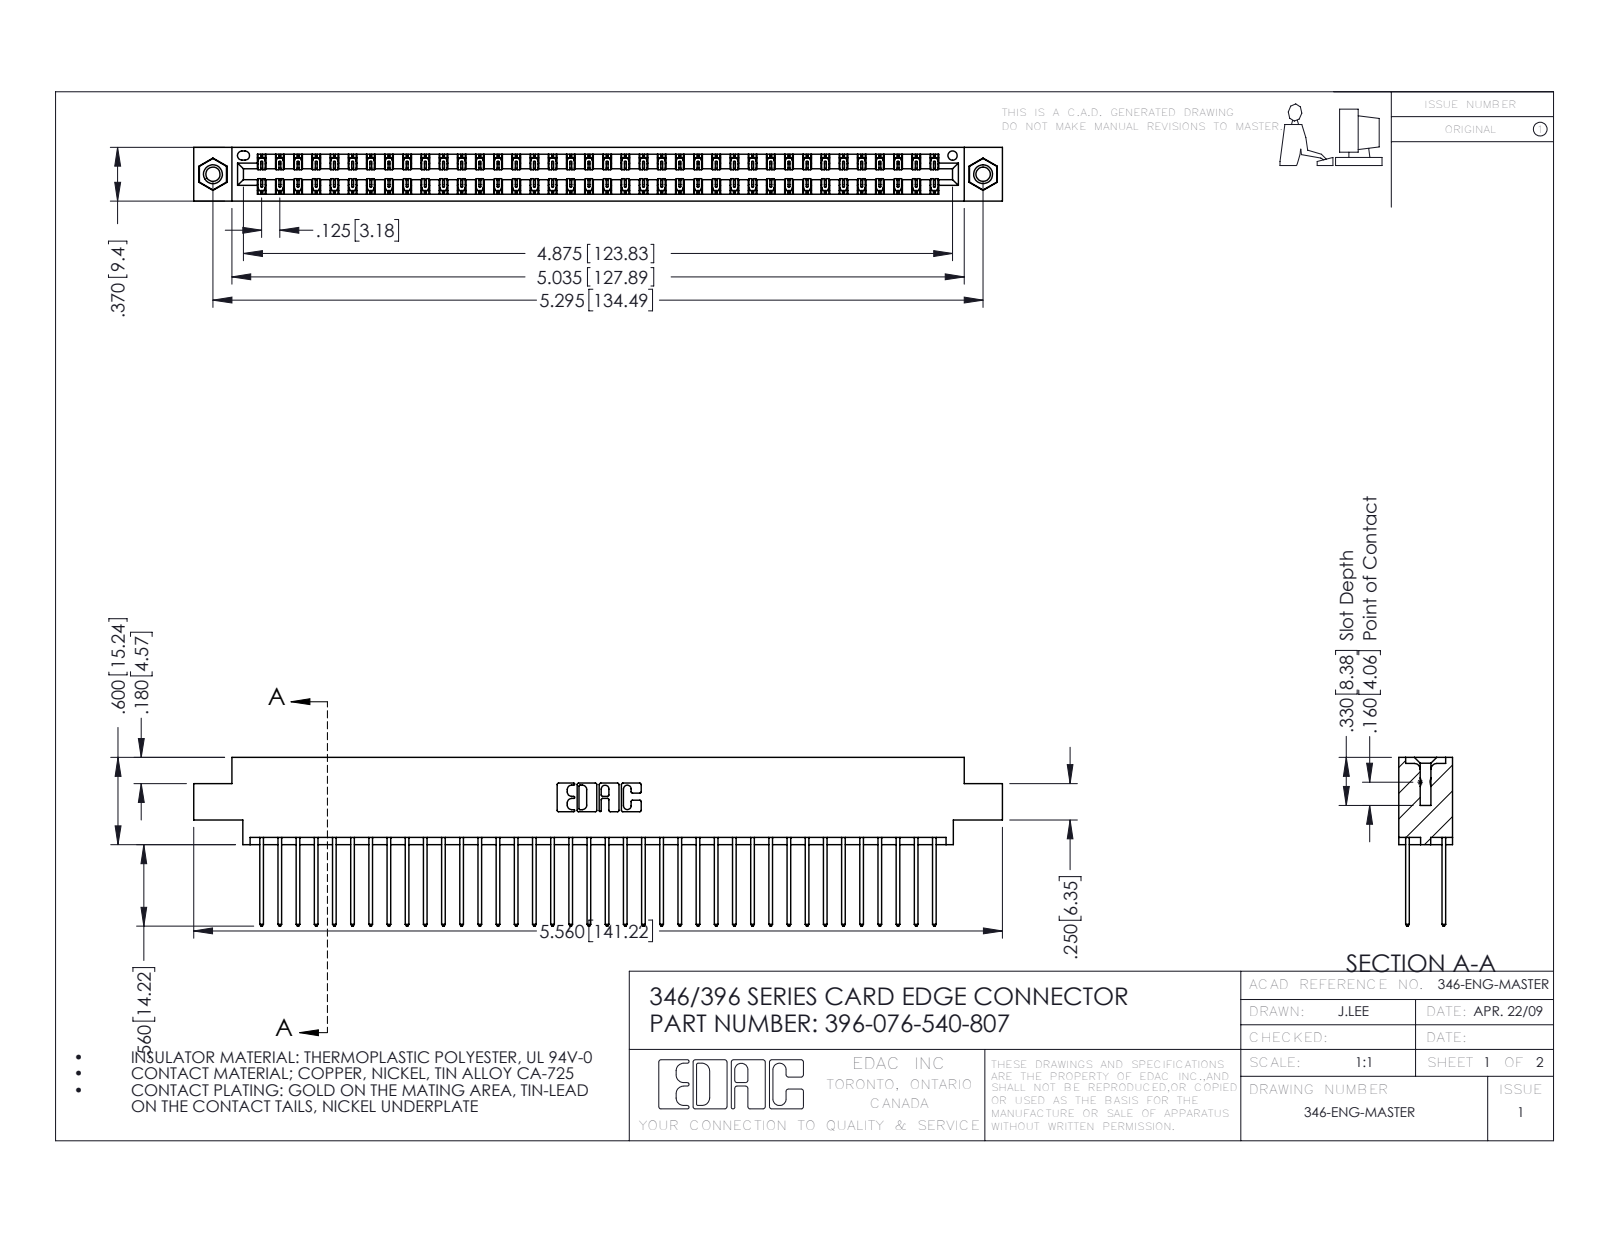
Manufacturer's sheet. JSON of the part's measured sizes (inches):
{"part_name": "346 Part_0.170 Offset - 0.156 Dia-TI; 345-292-001_345-293-140; 396-076-540-807; 345-250-001_345-250-005-103", "step_written_by": "SolidWorks 2016 (CONFIG_CONTROL_DESIGN)", "units": "inches", "bodies": {"solids": 79, "faces": 4138, "planar": 2772, "cylindrical": 1350, "other": 16}, "overall_size": [5.56, 1.16, 0.37], "volume_in3": 0.846, "surface_area_in2": 31.88, "round_holes": [[0.098, 2], [0.125, 2], [0.156, 2], [0.064, 1]], "round_bosses_or_shafts": [[0.155, 2]], "partial_cylinders_radius": [[0.006, 114], [0.01, 76], [0.01, 22], [0.007, 6], [0.031, 6], [0.026, 3], [0.014, 2], [0.022, 2]], "face_to_face_distances": [0.048, 0.322, 0.25, 0.072, 0.298, 0.025, 0.37, 0.275, 0.222, 0.148], "hole_center_spacings": [0.246, 5.086, 5.295]}
